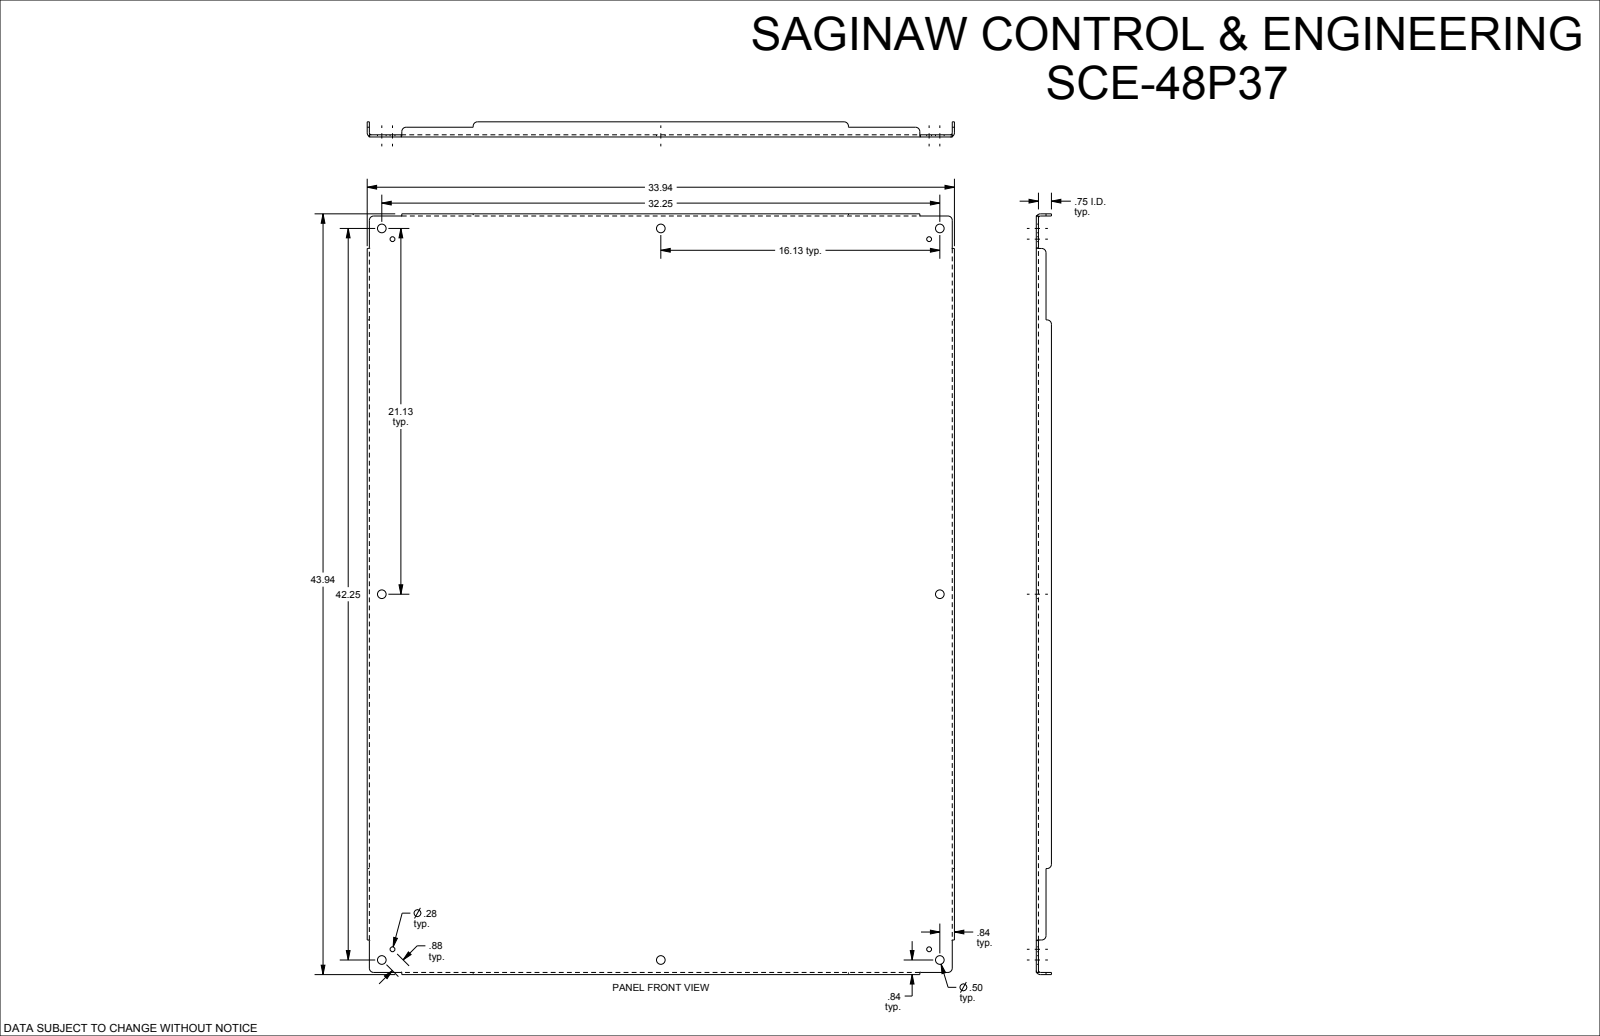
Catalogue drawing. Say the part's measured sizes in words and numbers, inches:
The part is named "SCE-48P37". Its 3-D file was written by "SolidWorks 2019 (CONFIG_CONTROL_DESIGN)". It is 1 solid with 110 faces: 46 planar, 40 cylindrical and 24 other. Overall it measures 43.938 by 33.938 by 0.875 inches. Its volume is 196.4 cubic inches and its surface area 3 164 square inches. Round holes: 8 of diameter 0.5, 4 of diameter 0.281. Partial cylindrical surfaces (rounded edges, fillets, slot ends): 12 of radius 0.25, 4 of radius 0.112, 4 of radius 0.237. The main face-to-face distances are 0.125, 0.125, 33.813, 43.813, 33.687, 33.938, 43.687, 43.938, 0.75, 0.875. The hole center spacings are 0.875, 15.519, 16.125, 20.516, 21.125, 26.576, 31.637, 37.696.
